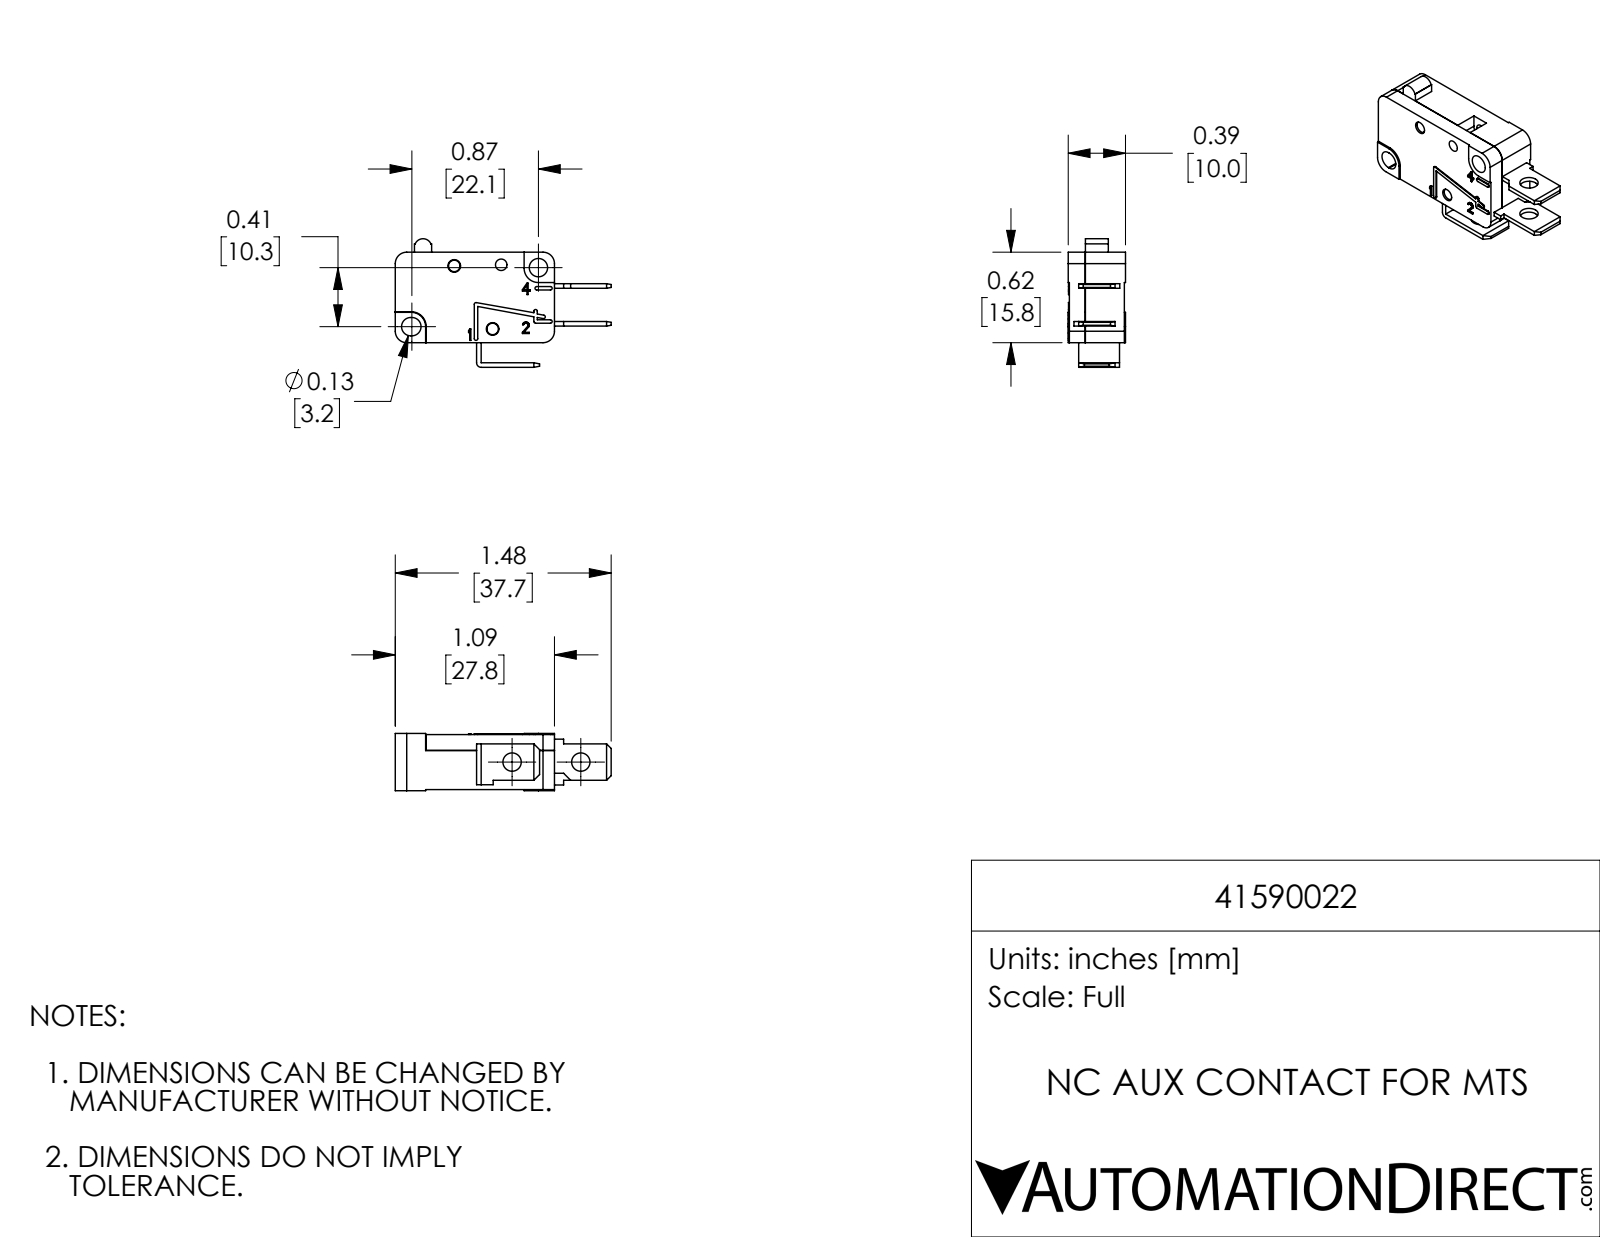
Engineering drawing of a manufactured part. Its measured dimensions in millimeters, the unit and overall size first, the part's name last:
Units: millimetres
Overall size (bounding box): 37.7 × 22.5 × 10
Round holes (diameter × count): ⌀3.2 ×3, ⌀2.2 ×2, ⌀2 ×1
Round bosses / shafts (diameter × count): ⌀2 ×2
Partial cylindrical surfaces — rounded edges, fillets, slot ends (radius × count): R0.3 ×9, R2 ×4, R1.6 ×2, R2.5 ×2, R0.8 ×1, R1.5 ×1, R1.7 ×1, R2.6 ×1
Main face-to-face distances: 6.8, 6.9, 9.6, 2.8, 2.7, 15.8, 0.8, 27.8, 6.6, 13.8
Hole centre spacings: 6.5, 8.2, 11.3, 12, 12.9, 13.4, 14.7
Volume: 4 130 mm³ · Surface area: 3 332 mm²
Bodies: 3 solids, 215 faces (153 planar, 60 cylindrical, 2 other)
Part name (STEP PRODUCT): 41590022
STEP written by: SolidWorks 2017 (AUTOMOTIVE_DESIGN)
